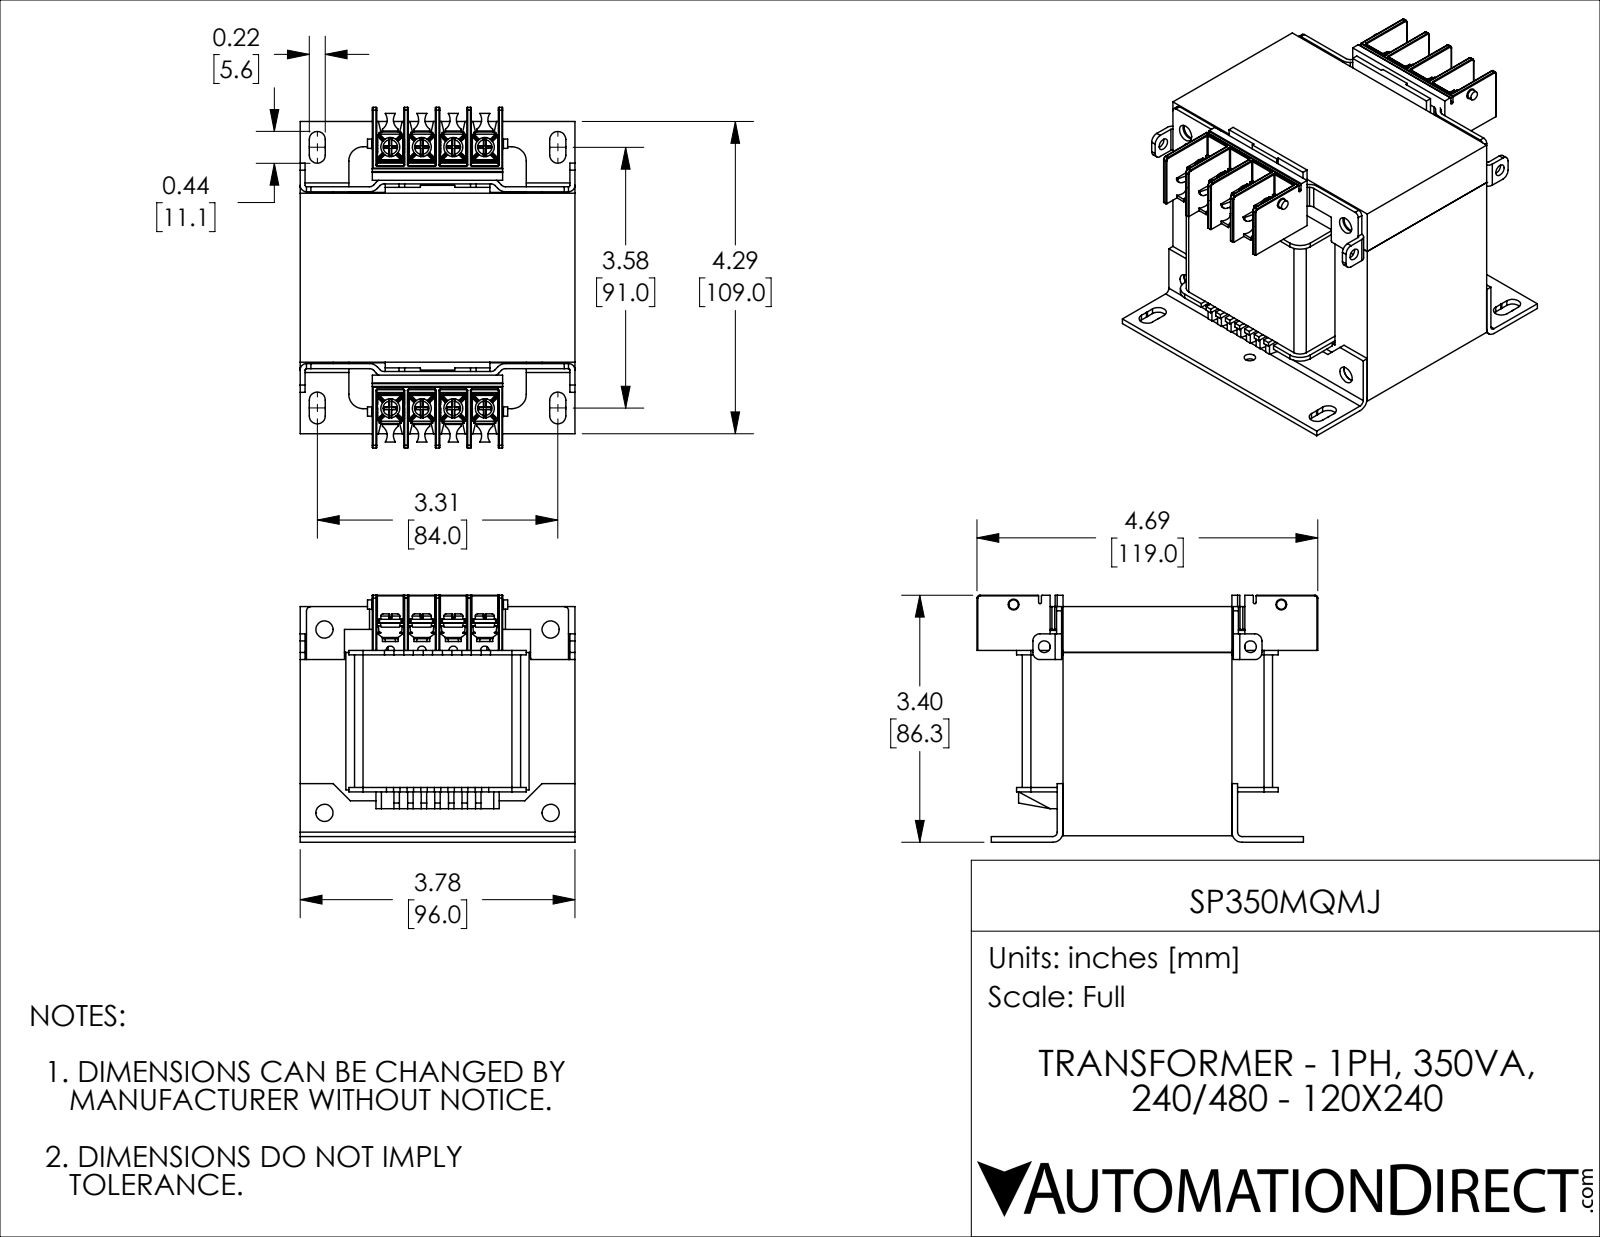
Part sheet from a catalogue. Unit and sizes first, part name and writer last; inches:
Units: inches
Overall size (bounding box): 4.685 × 3.78 × 3.396
Round holes (diameter × count): ⌀0.157 ×10, ⌀0.105 ×8, ⌀0.138 ×8, ⌀0.236 ×4, ⌀0.161 ×2
Round bosses / shafts (diameter × count): ⌀0.262 ×8, ⌀0.24 ×8, ⌀0.168 ×8, ⌀0.11 ×8, ⌀0.128 ×2
Partial cylindrical surfaces — rounded edges, fillets, slot ends (radius × count): R0.01 ×62, R0.005 ×52, R0.012 ×42, R0.029 ×32, R0.157 ×16, R0.035 ×12, R0.065 ×12, R0.079 ×10
Main face-to-face distances: 0.63, 2.52, 3.15, 2.402, 1.26, 0.079, 2.323, 1.89, 0.748, 3.031
Hole centre spacings: 0.433, 0.866, 3.607, 1.299, 3.581, 3.684, 3.597, 3.617
Volume: 33.57 in³ · Surface area: 220.2 in²
Bodies: 41 solids, 3229 faces (1997 planar, 934 cylindrical, 298 other)
Part name (STEP PRODUCT): SP350MQMJ
STEP written by: SolidWorks 2018 (AUTOMOTIVE_DESIGN)
